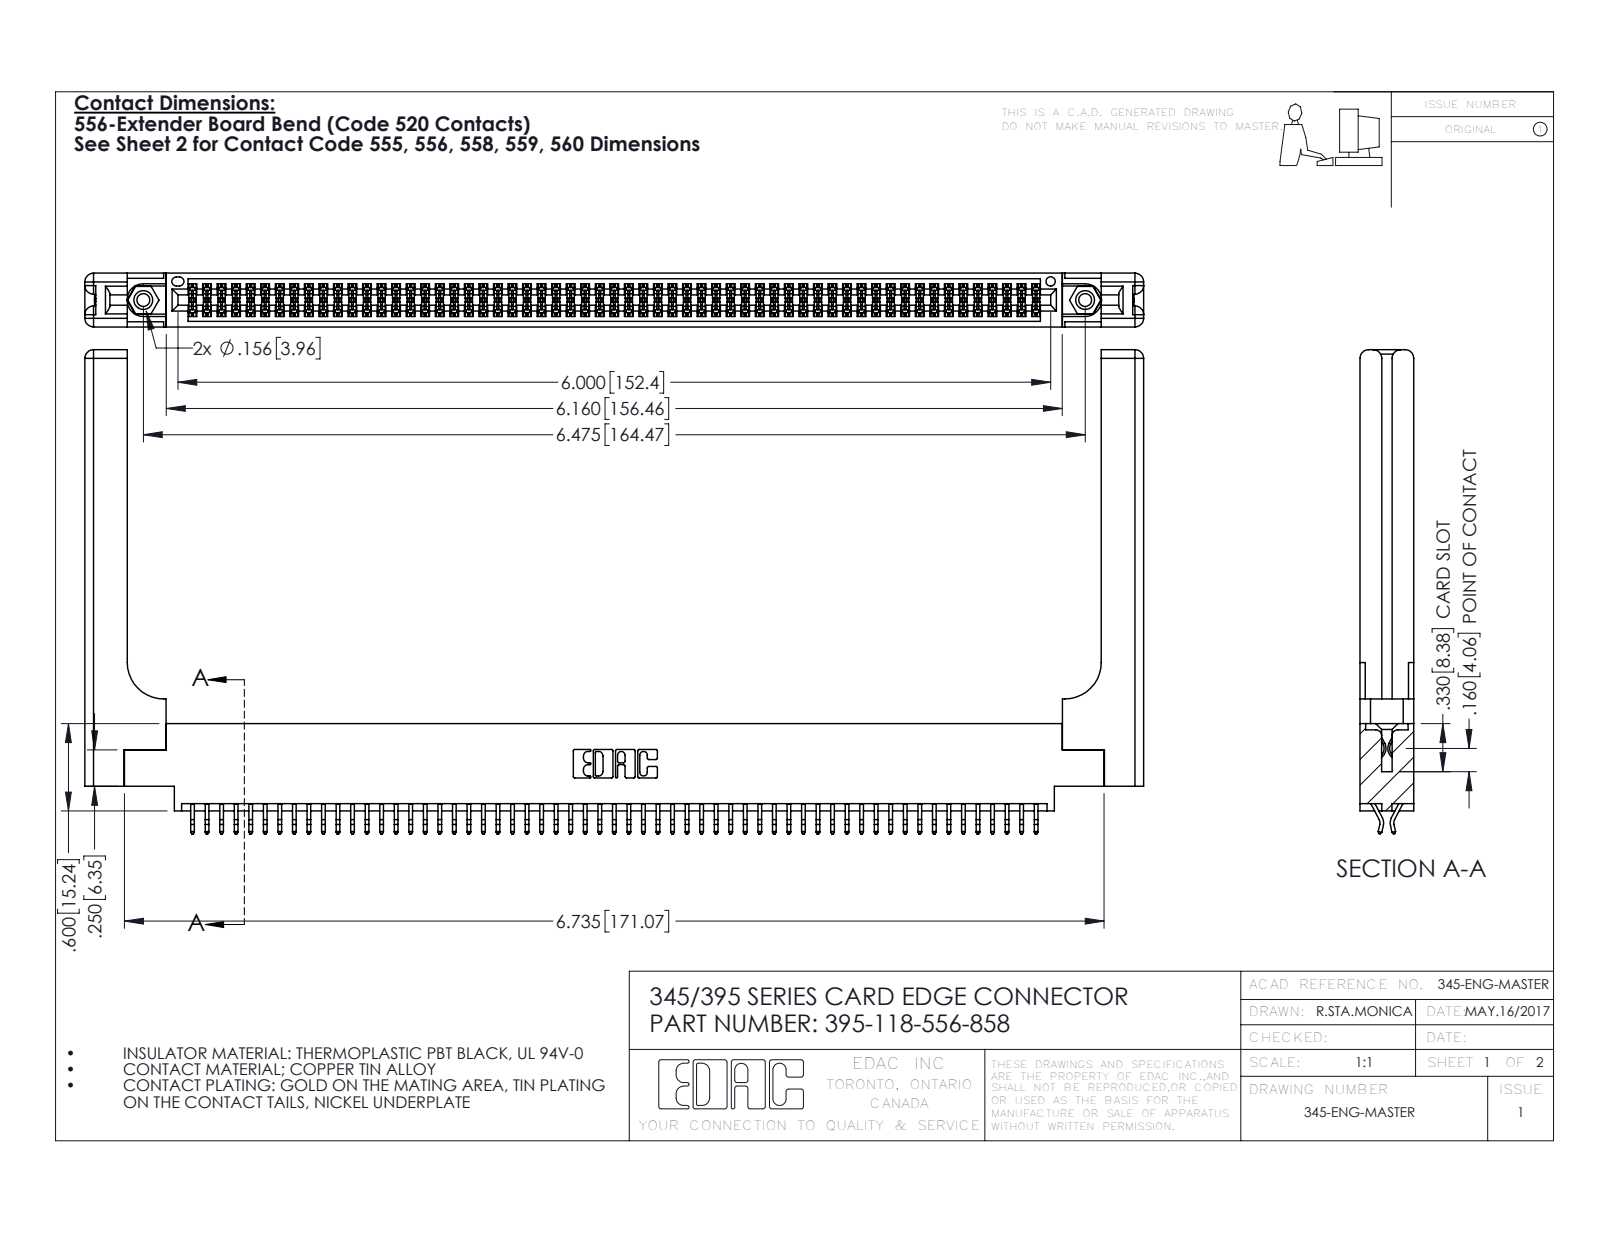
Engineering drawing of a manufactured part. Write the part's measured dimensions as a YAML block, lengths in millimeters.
part_name: "395-118-556-858; 345-250-001_345-250-001-102; 345-220-058_345-220-058; 345 Part_0.170 Offset - 0.156 Dia-TH (+1 more)"
step_written_by: "SolidWorks 2016 (CONFIG_CONTROL_DESIGN)"
units: millimeters
bodies: {solids: 123, faces: 6994, planar: 4598, cylindrical: 2336, other: 60}
overall_size: [184.9, 84.5, 9.4]
volume: 26480
surface_area: 32030
round_holes:
  - {diameter: 2.3, count: 2}
  - {diameter: 3.2, count: 2}
  - {diameter: 4, count: 2}
  - {diameter: 1.6, count: 1}
round_bosses_or_shafts:
  - {diameter: 3.9, count: 2}
partial_cylinders:
  - {radius: 0.2, count: 177}
  - {radius: 0.3, count: 22}
  - {radius: 1.5, count: 16}
  - {radius: 0.2, count: 6}
  - {radius: 0.8, count: 6}
  - {radius: 0.7, count: 3}
  - {radius: 0.3, count: 2}
  - {radius: 0.4, count: 2}
face_to_face_distances: [1.8, 9.4, 7.6, 0.6, 2.5, 6.9, 5.1, 5.7, 4.4, 3.8]
hole_center_spacings: [6.9, 158.5, 164.5]
